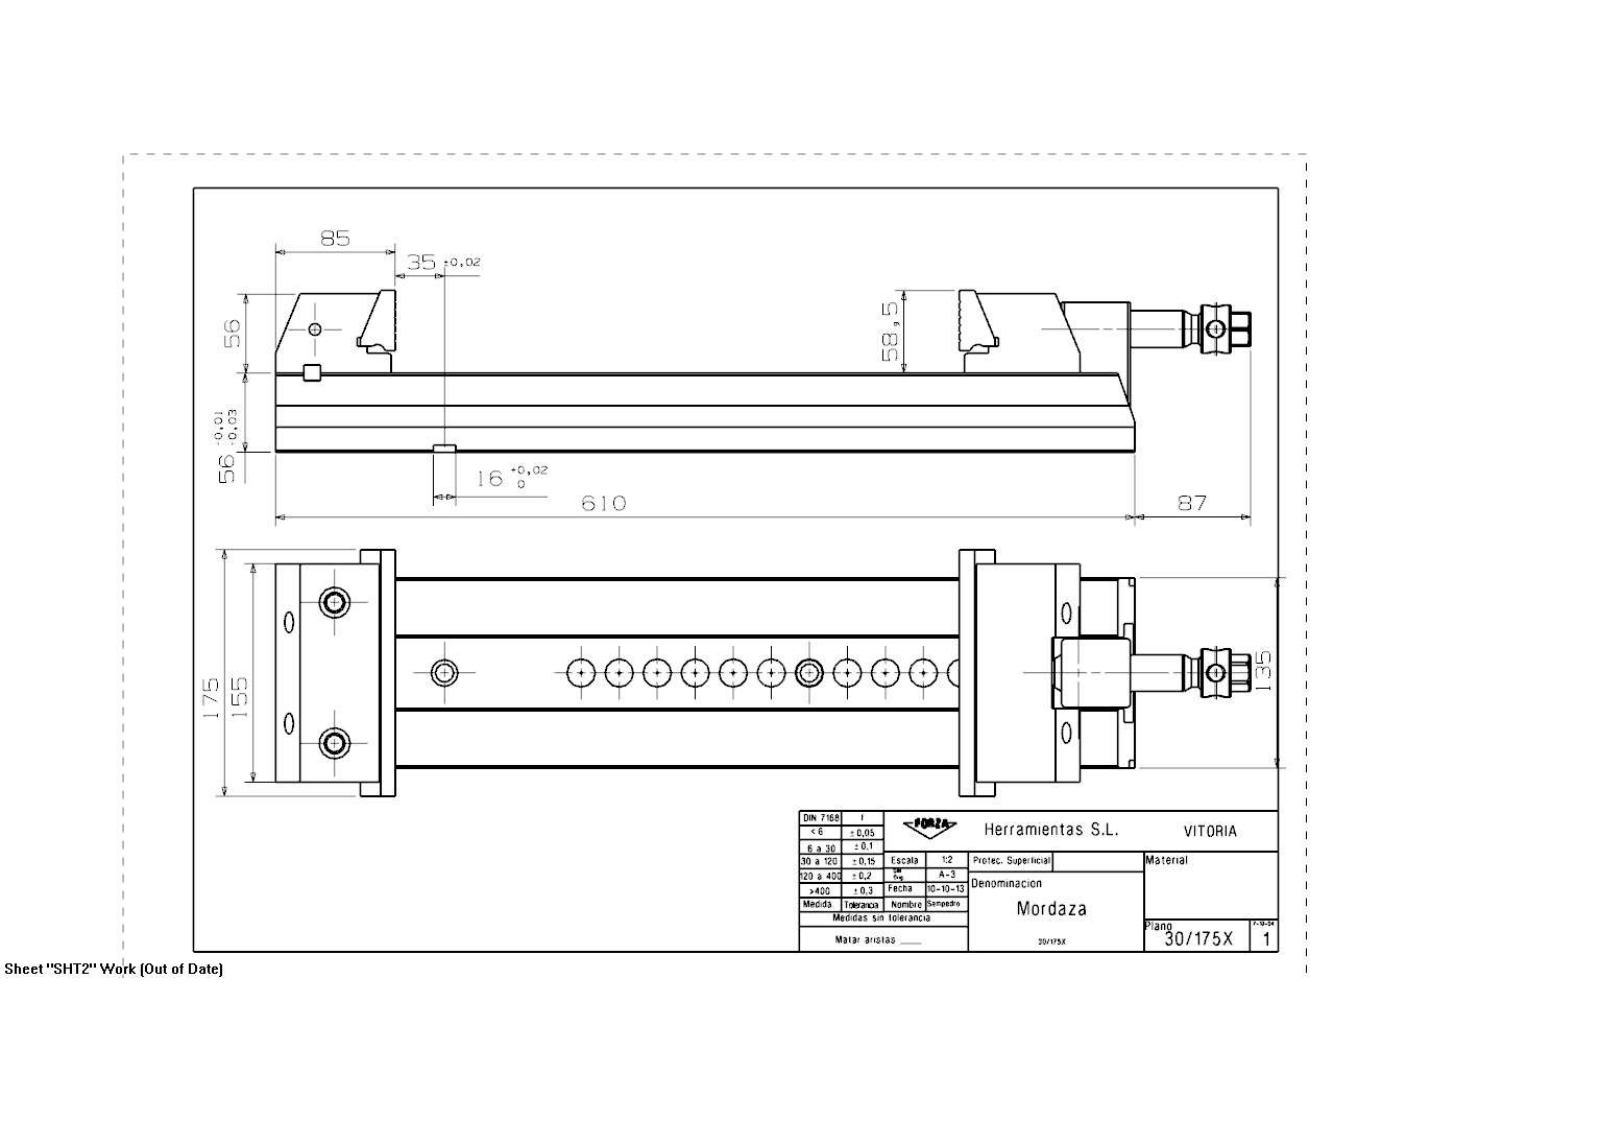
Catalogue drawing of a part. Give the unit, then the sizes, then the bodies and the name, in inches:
Units: inches
Overall size (bounding box): 27.253 × 6.89 × 4.508
Round holes (diameter × count): ⌀0.512 ×6, ⌀0.591 ×6, ⌀0.748 ×6, ⌀0.204 ×5, ⌀0.394 ×4, ⌀0.417 ×4, ⌀0.472 ×4, ⌀0.346 ×3, ⌀0.275 ×2, ⌀0.335 ×2, ⌀0.487 ×2, ⌀0.866 ×2
Round bosses / shafts (diameter × count): ⌀1.339 ×1, ⌀1.331 ×1, ⌀1.024 ×1, ⌀0.787 ×1, ⌀0.65 ×1
Partial cylindrical surfaces — rounded edges, fillets, slot ends (radius × count): R0.315 ×4, R0.787 ×4, R0.063 ×2, R0.236 ×2, R0.276 ×2, R0.157 ×1, R0.354 ×1, R0.413 ×1
Main face-to-face distances: 2.205, 1.252, 0.953, 1.28, 4.035, 5.315, 1.063, 0.039, 0.913, 2.165
Hole centre spacings: 2.835, 0.256, 3.091, 4.176, 0.048, 1.093, 1.181, 1.347
Volume: 295.8 in³ · Surface area: 922.9 in²
Bodies: 14 solids, 511 faces (316 planar, 110 cylindrical, 85 other)
Part name (STEP PRODUCT): 30_175X_Mordaza
STEP written by: SIEMENS PLM Software NX 7.5 (CONFIG_CONTROL_DESIGN)
